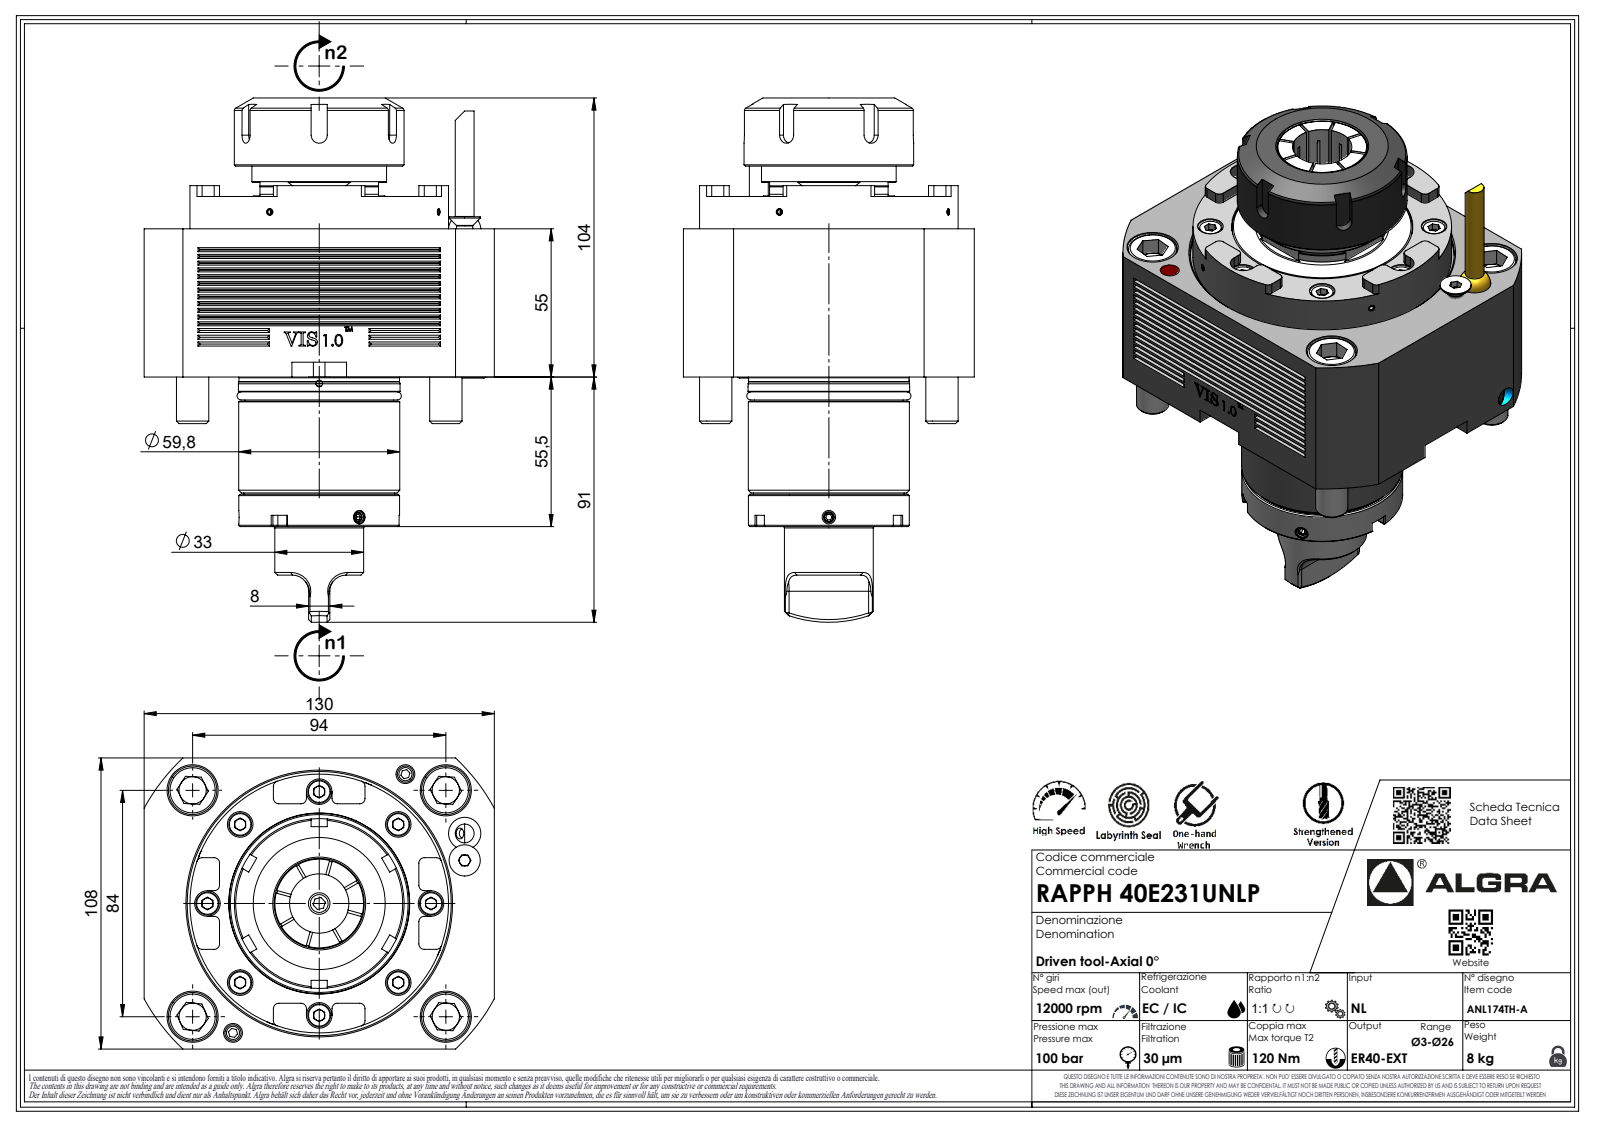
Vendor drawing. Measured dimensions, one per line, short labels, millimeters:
name: RAPPH40E231UNLP
written by: SolidWorks 2023 (AUTOMOTIVE_DESIGN)
unit: mm
bodies: 1 solid, 511 faces (315 planar, 89 cylindrical, 107 other)
size: 194.21 × 130 × 108
volume: 1 117 000 mm³; area: 82 507 mm²
holes: 1× ⌀2.1, 1× ⌀4
bosses: 4× ⌀12, 1× ⌀96, 1× ⌀63, 1× ⌀60, 1× ⌀59.8, 1× ⌀50, 1× ⌀33, 1× ⌀7
rounds: 25× R2, 7× R0.33, 7× R0.52, 7× R3.7, 6× R6, 4× R4.75, 3× R3, 1× R0.21
face distances: 55, 108, 67, 12, 130, 55.5, 110.5, 122.5, 158.71, 103.21
